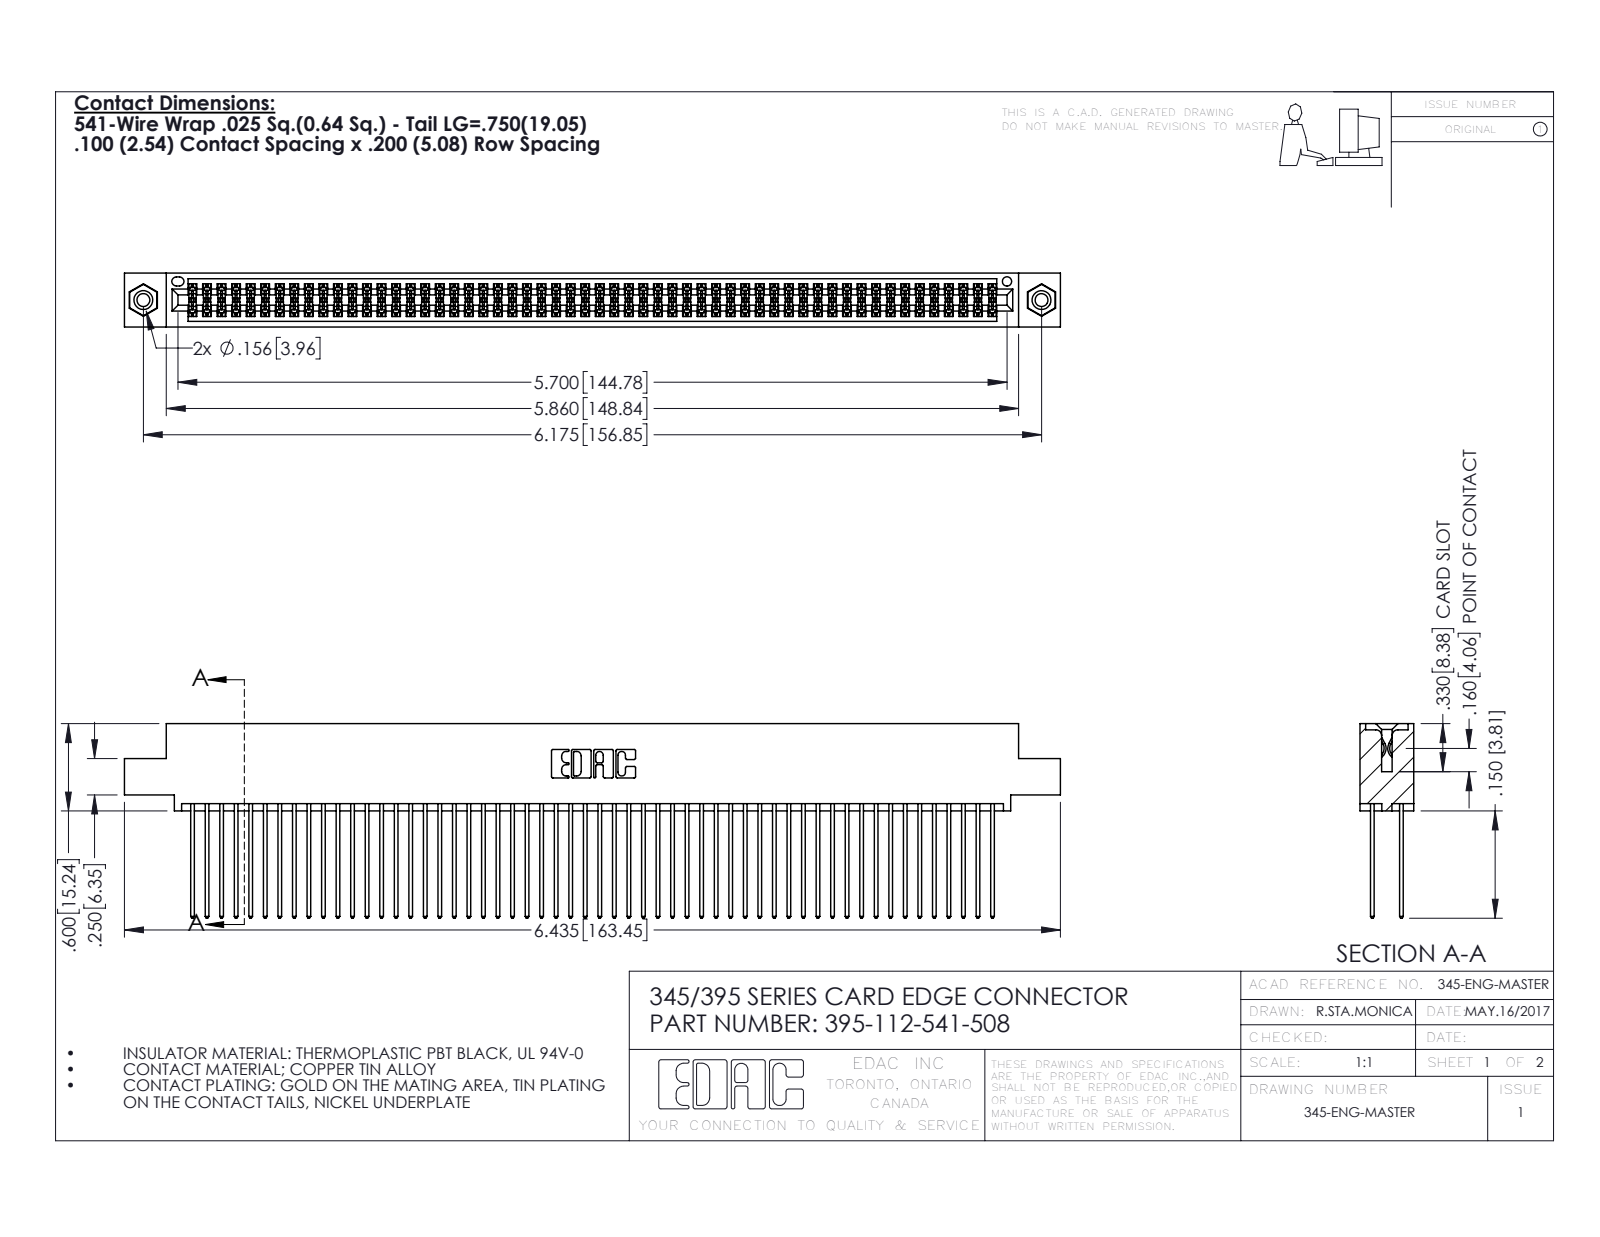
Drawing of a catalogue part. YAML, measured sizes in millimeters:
part_name: "345 Part_0.110 Offset - 0.156 Dia-TI; 345-292-001_345-293-141; 395-112-541-508; 345-250-001_345-250-003-102"
step_written_by: "SolidWorks 2016 (CONFIG_CONTROL_DESIGN)"
units: millimeters
bodies: {solids: 115, faces: 5790, planar: 3812, cylindrical: 1962, other: 16}
overall_size: [163.4, 34, 9.4]
volume: 16570
surface_area: 27890
round_holes:
  - {diameter: 2.3, count: 2}
  - {diameter: 3.2, count: 2}
  - {diameter: 4, count: 2}
  - {diameter: 1.6, count: 1}
round_bosses_or_shafts:
  - {diameter: 3.9, count: 2}
partial_cylinders:
  - {radius: 0.2, count: 168}
  - {radius: 0.3, count: 112}
  - {radius: 0.3, count: 22}
  - {radius: 0.2, count: 6}
  - {radius: 0.8, count: 6}
  - {radius: 0.7, count: 3}
  - {radius: 0.4, count: 2}
  - {radius: 0.5, count: 2}
face_to_face_distances: [1.8, 7.6, 5.1, 2.5, 6.9, 0.6, 5.7, 9.4, 4.4, 3.8]
hole_center_spacings: [6.9, 150.9, 156.8]
